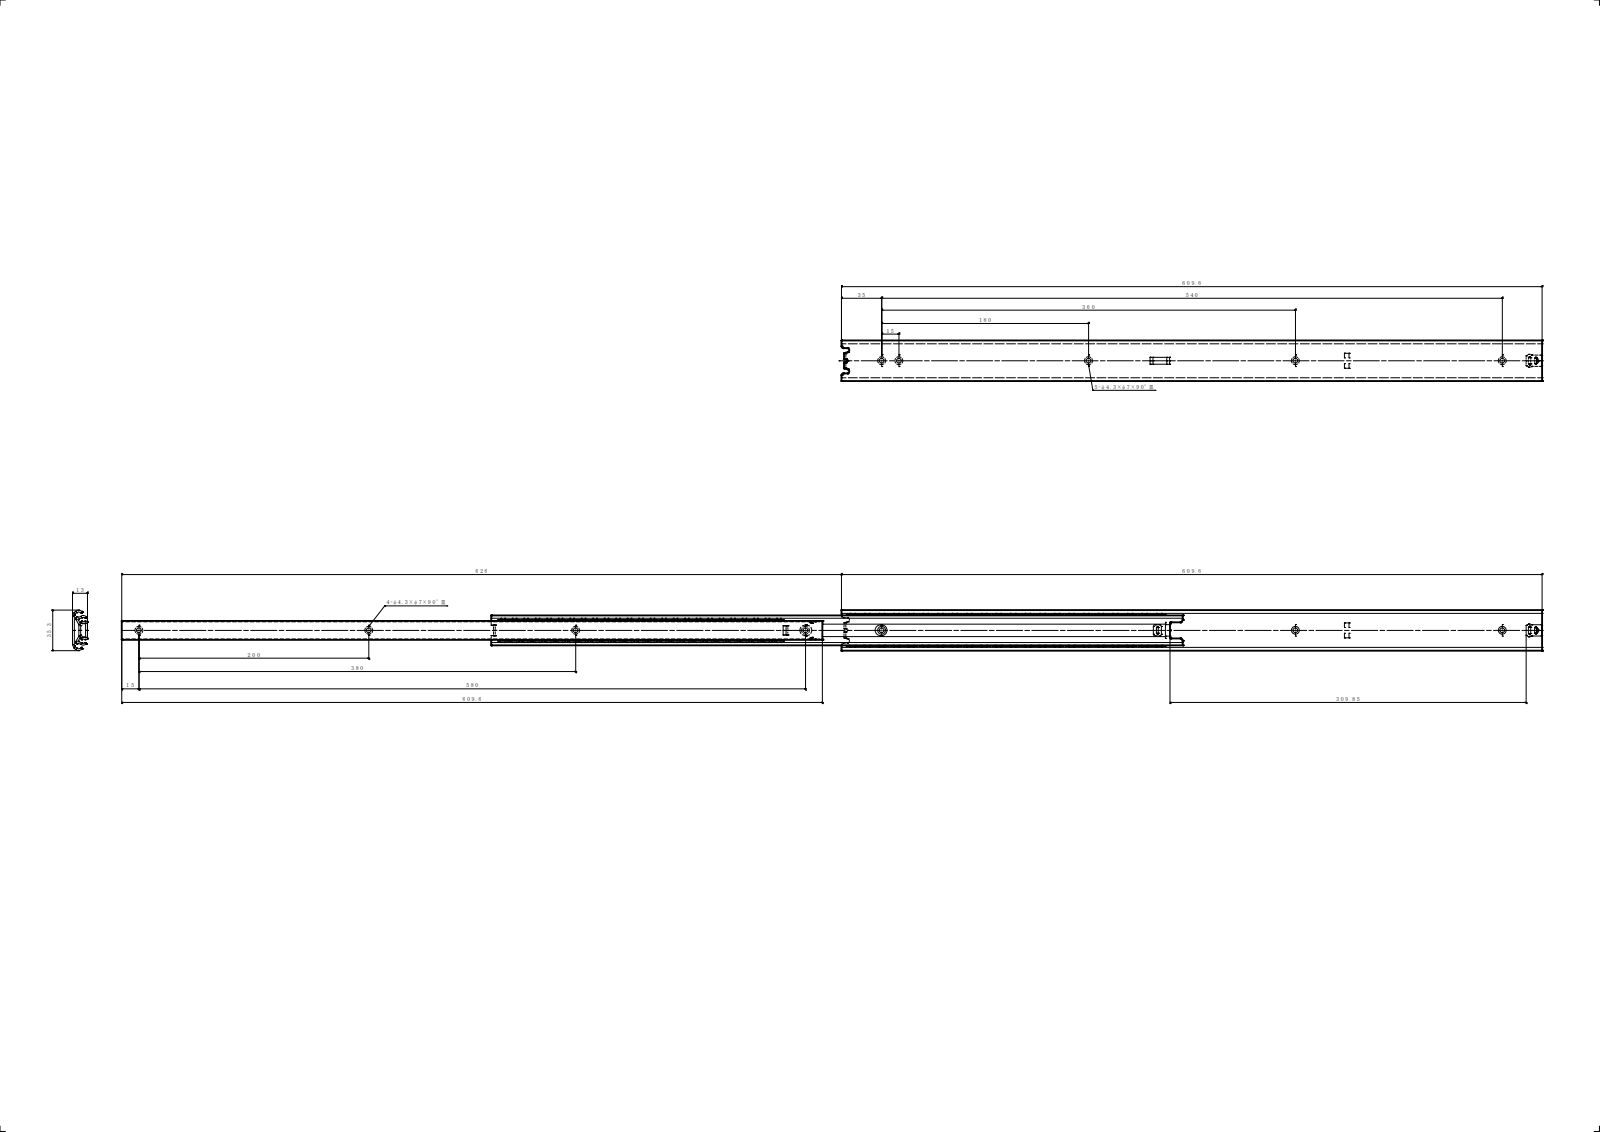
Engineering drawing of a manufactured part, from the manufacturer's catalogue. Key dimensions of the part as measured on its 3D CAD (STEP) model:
Part name (STEP PRODUCT): PN32; C351-24; C351-24 CM; C351-24 OM (+2 more)
STEP written by: SolidWorks 2019 (CONFIG_CONTROL_DESIGN)
Units: millimetres
Bodies: 5 solids, 300 faces (144 planar, 136 cylindrical, 20 other)
Overall size (bounding box): 1235.89 × 35.3 × 13
Volume: 106 924 mm³ · Surface area: 138 465 mm²
Round holes (diameter × count): ⌀4.3 ×9, ⌀4.5 ×1
Partial cylindrical surfaces — rounded edges, fillets, slot ends (radius × count): R0.5 ×21, R3 ×10, R1.5 ×8, R0.3 ×6, R2 ×6, R0.8 ×4, R1 ×4, R1.6 ×4
Main face-to-face distances: 1.6, 11.4, 5.4, 6, 13, 9.8, 3.8, 7.6, 7, 4.4
Hole centre spacings: 180, 200, 360, 380, 446.29, 626.29, 806.29, 15
